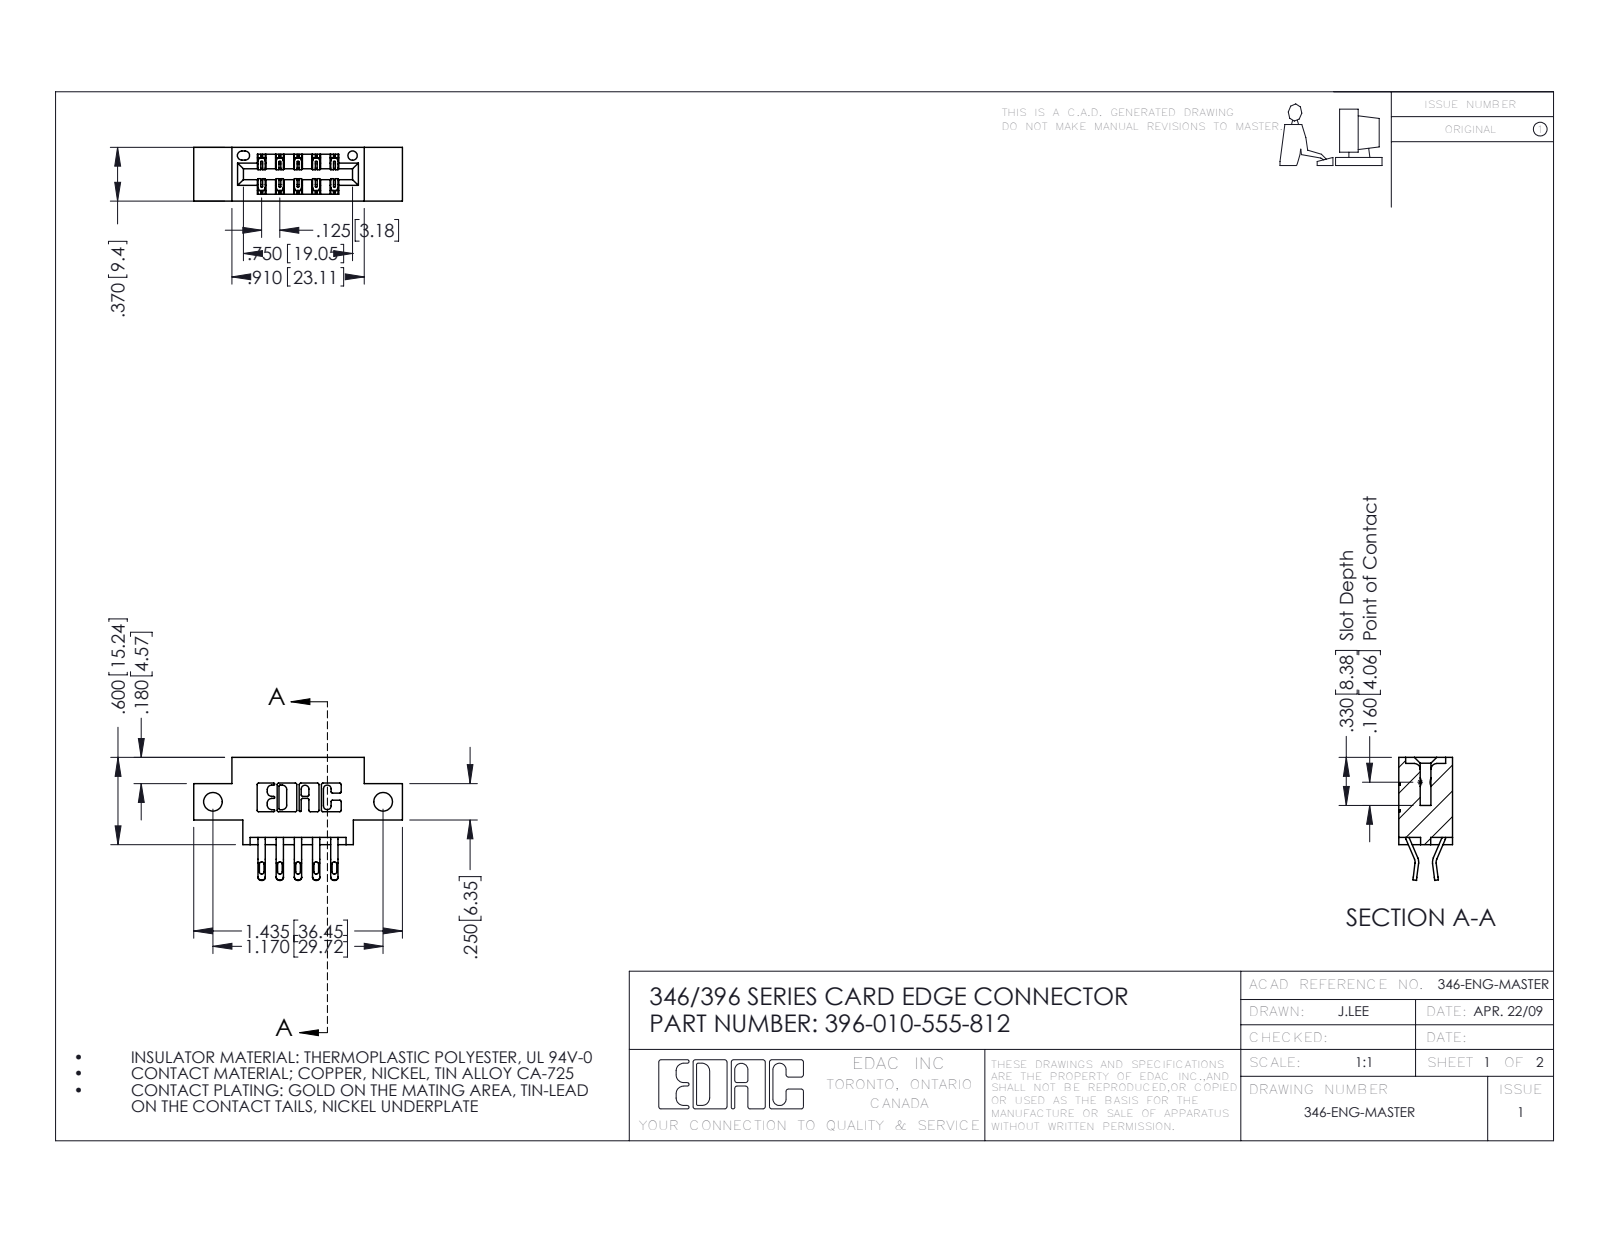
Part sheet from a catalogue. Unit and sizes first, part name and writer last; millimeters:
Units: millimetres
Overall size (bounding box): 36.4 × 21.5 × 9.4
Round holes (diameter × count): ⌀3.3 ×2, ⌀1.6 ×1
Partial cylindrical surfaces — rounded edges, fillets, slot ends (radius × count): R0.3 ×22, R0.4 ×20, R0.5 ×20, R0.2 ×15, R0.2 ×6, R0.8 ×6, R0.7 ×3, R0.3 ×2
Main face-to-face distances: 6.4, 9.4, 1.2, 8.2, 3.2, 3.8, 5.6, 2.5, 4.4, 0.6
Hole centre spacings: 29.7
Volume: 3 050 mm³ · Surface area: 3 762 mm²
Bodies: 11 solids, 706 faces (410 planar, 296 cylindrical, 0 other)
Part name (STEP PRODUCT): 346 Part_0.170 Offset - Side Mount; 396-010-555-812; 345-292-001_555 Tail
STEP written by: SolidWorks 2016 (CONFIG_CONTROL_DESIGN)
